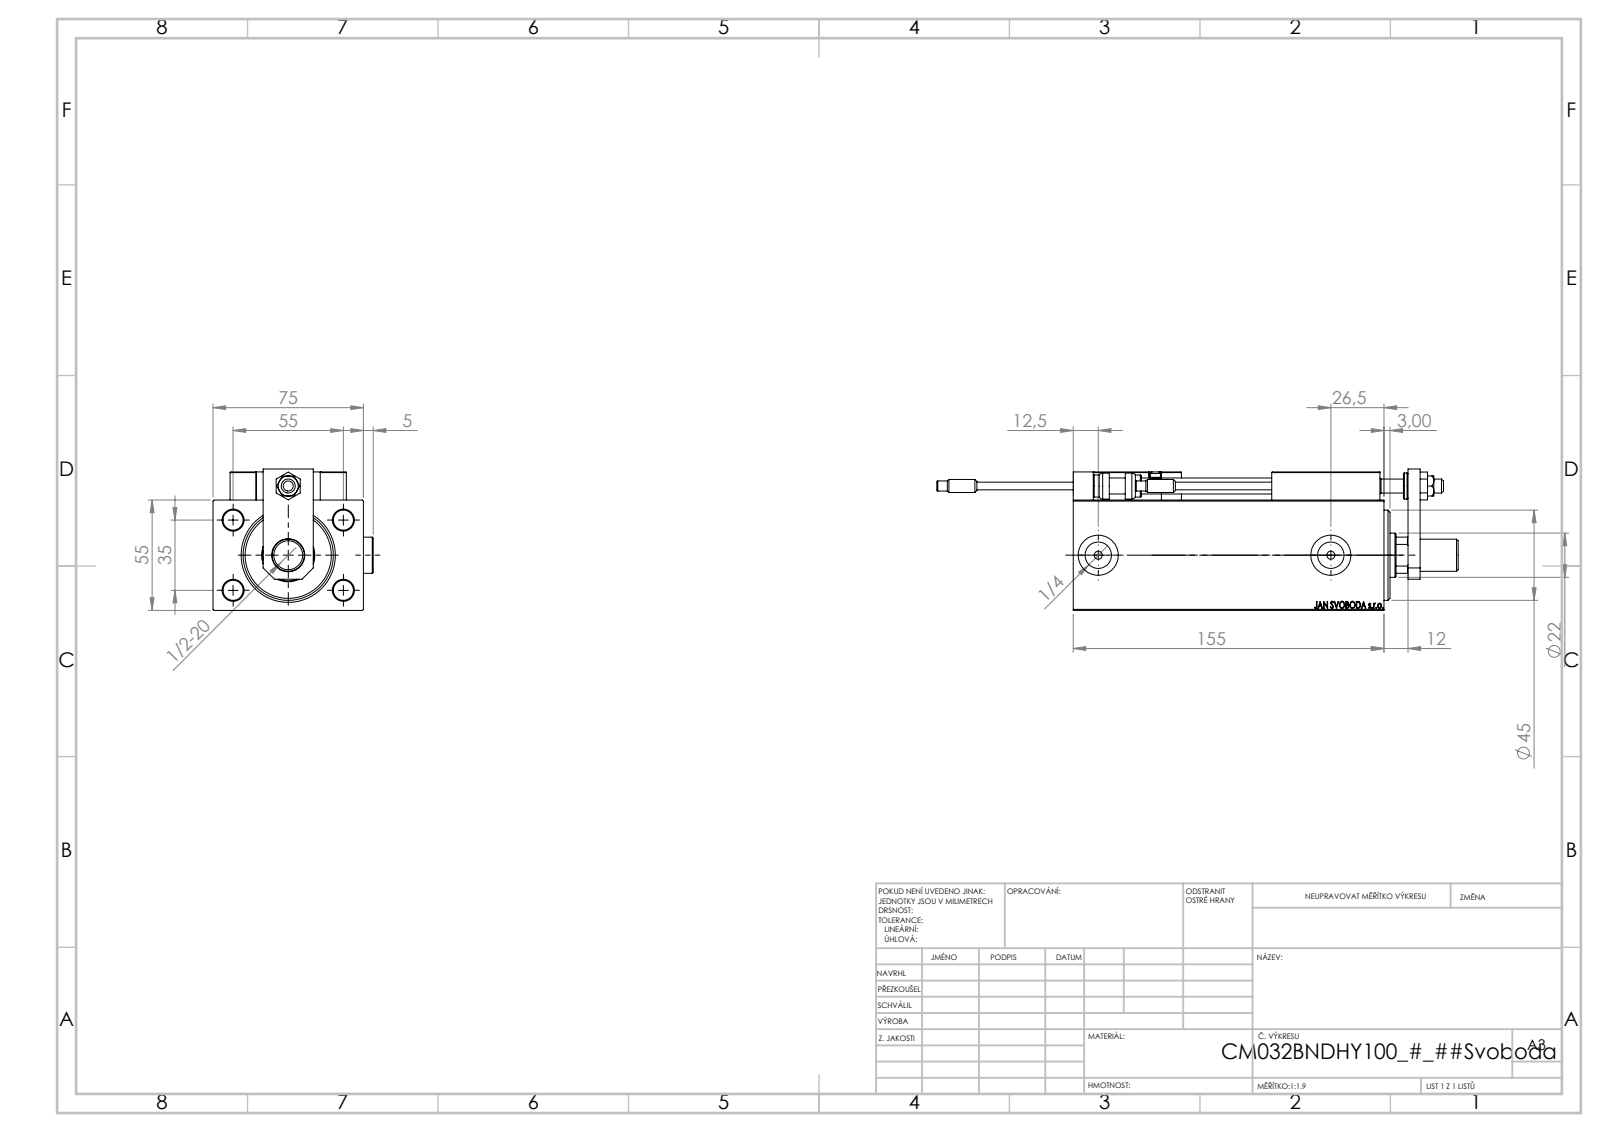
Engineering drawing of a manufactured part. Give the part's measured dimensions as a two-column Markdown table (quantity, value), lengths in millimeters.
| quantity | value |
| --- | --- |
| part name | V450CM_B_Body; NUT_D12; V450CM_MALE_METRIC; ALLEN BOLT D8 (+7 more) |
| STEP written by | SolidWorks 2019 (CONFIG_CONTROL_DESIGN) |
| units | millimeters |
| bodies | 27 solids, 1407 faces (600 planar, 212 cylindrical, 595 other) |
| overall size | 260 × 79.9 × 70.5 |
| volume | 641 881 mm³ |
| surface area | 120 624 mm² |
| round holes (diameter × count) | 4 × 6, 8 × 5, 3.2 × 4, 10 × 4, 5 × 2, 13.16 × 2, 20 × 2, 7 × 1, 10.5 × 1, 16.5 × 1, 22 × 1, 25.5 × 1 |
| round bosses / shafts (diameter × count) | 5 × 4, 18 × 2, 6.5 × 2, 3.8 × 2, 16 × 1, 14 × 1, 13 × 1, 11 × 1 |
| partial cylindrical surfaces (radius × count) | 0.3 × 30, 3 × 2, 10.5 × 1 |
| main face-to-face distances | 55, 75, 10, 12, 14, 5, 7, 69, 25, 155 |
| hole center spacings | 32.6, 11.37, 20, 29.59, 29.69, 32.33, 35, 36.06 |
